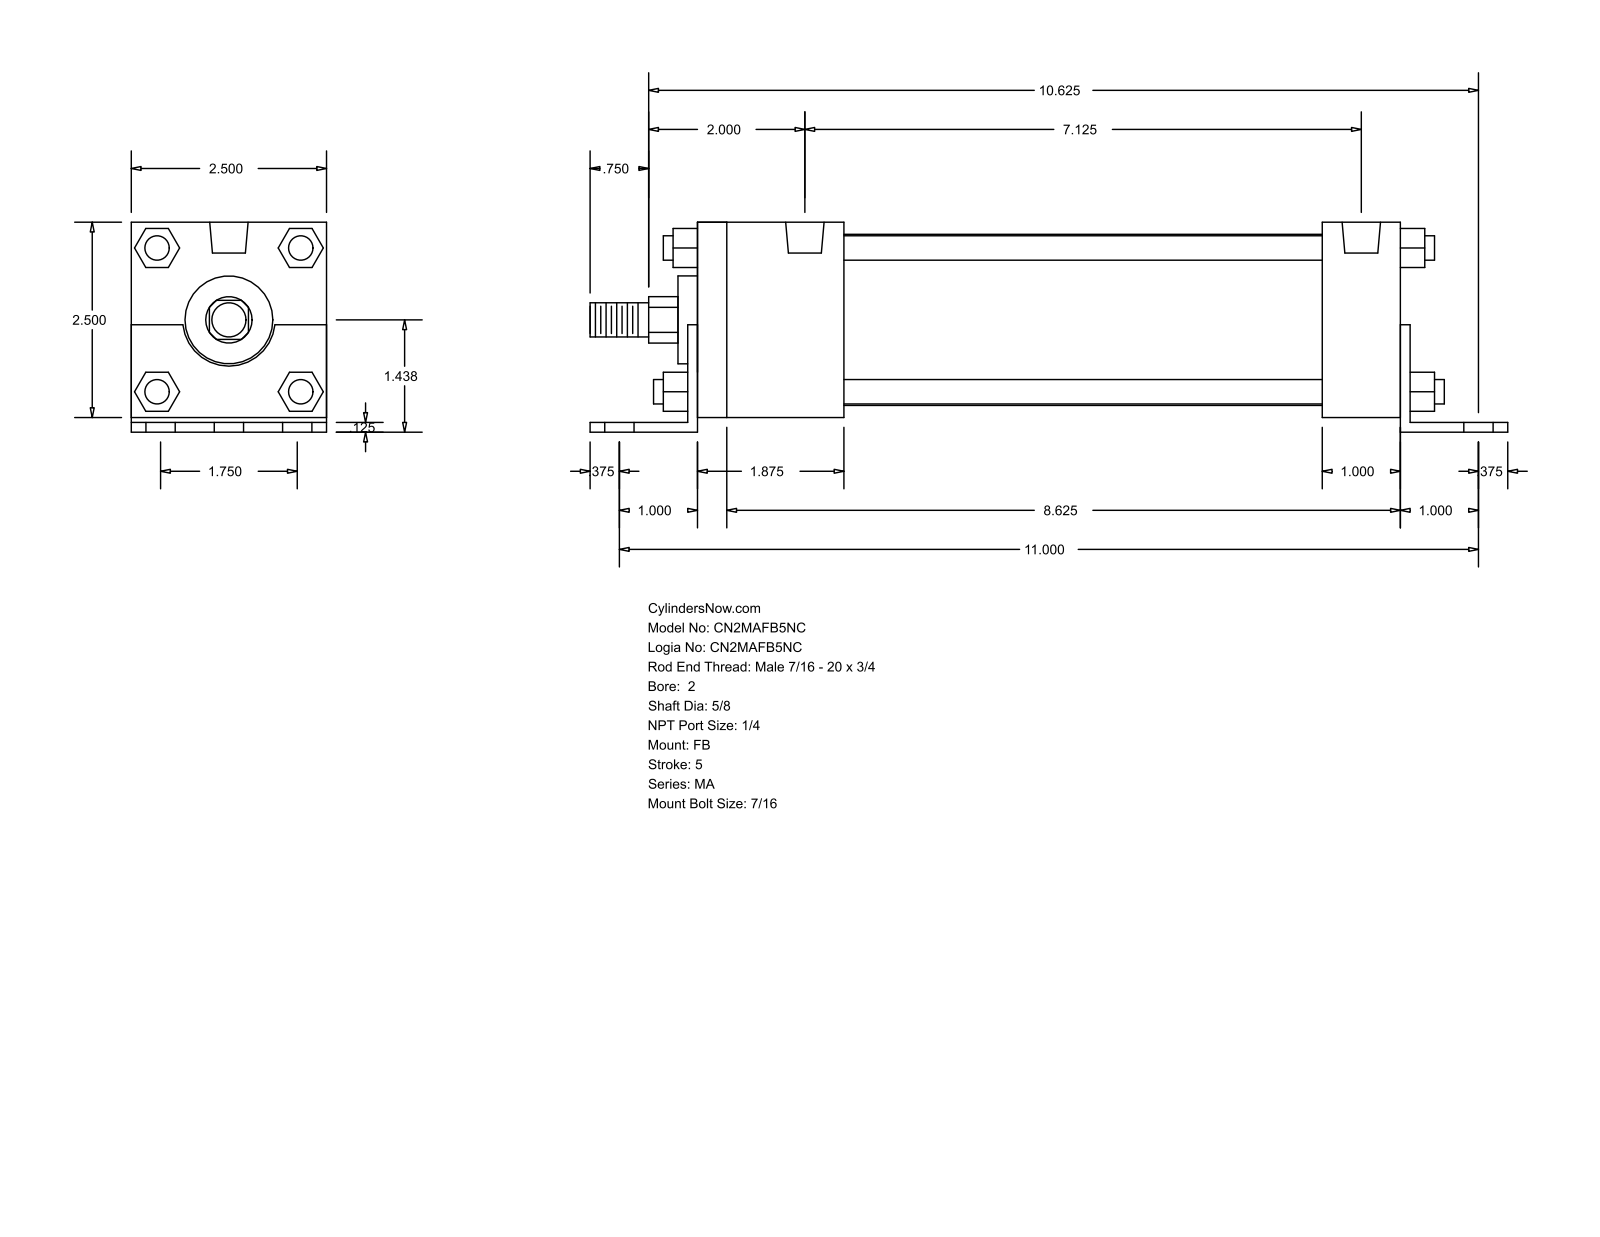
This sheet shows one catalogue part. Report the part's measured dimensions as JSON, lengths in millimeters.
{"part_name": "MA_FB__0200_0.625", "step_written_by": "GSSL Pune (CONFIG_CONTROL_DESIGN)", "units": "millimeters", "bodies": {"solids": 0, "faces": 140, "planar": 105, "cylindrical": 35, "other": 0}, "overall_size": [298.45, 68.26, 63.5], "round_holes": [[11.11, 6], [7.94, 4], [12.49, 2]], "round_bosses_or_shafts": [[7.94, 4], [55.63, 1], [28.57, 1], [15.88, 1], [11.11, 1]], "partial_cylinders_radius": [[7.54, 1], [15.05, 1]], "face_to_face_distances": [63.5, 4.76, 3.17, 68.26, 1.59, 3.18, 65.09, 231.77, 228.59, 28.58], "hole_center_spacings": [22.23, 280.29, 279.41, 44.11, 44.46, 64.3, 180.98, 220.2]}
